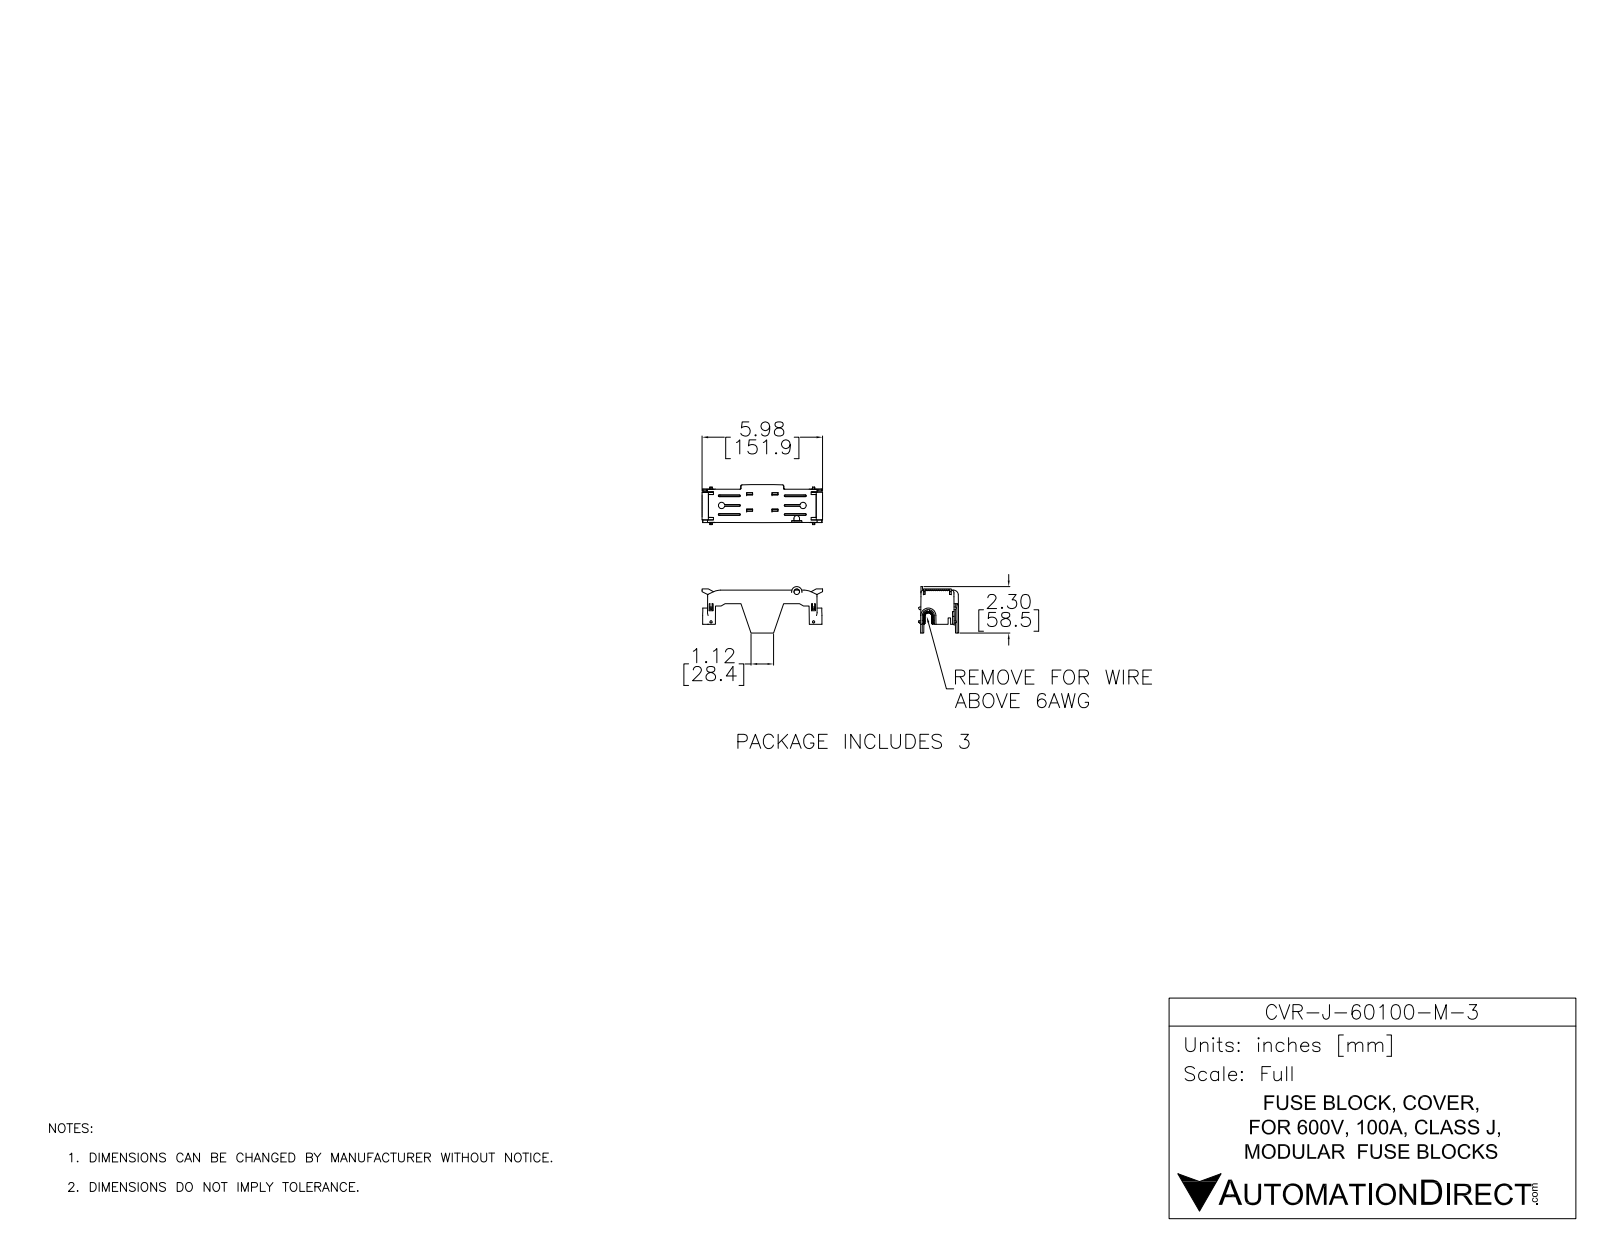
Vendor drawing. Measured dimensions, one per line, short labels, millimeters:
name: CVR-J-60100-M-3
written by: SolidWorks 2017 (AUTOMOTIVE_DESIGN)
unit: mm
bodies: 1 solid, 1410 faces (917 planar, 102 cylindrical, 391 other)
size: 151.9 × 58.5 × 50.4
volume: 41 790 mm³; area: 45 170 mm²
rounds: 19× R1, 14× R3, 6× R0.8, 4× R1.5, 2× R0.3, 2× R0.5, 2× R3.5, 2× R4.3
face distances: 2, 5.5, 3.5, 7.5, 3, 8.8, 5, 6, 3.6, 1.5
